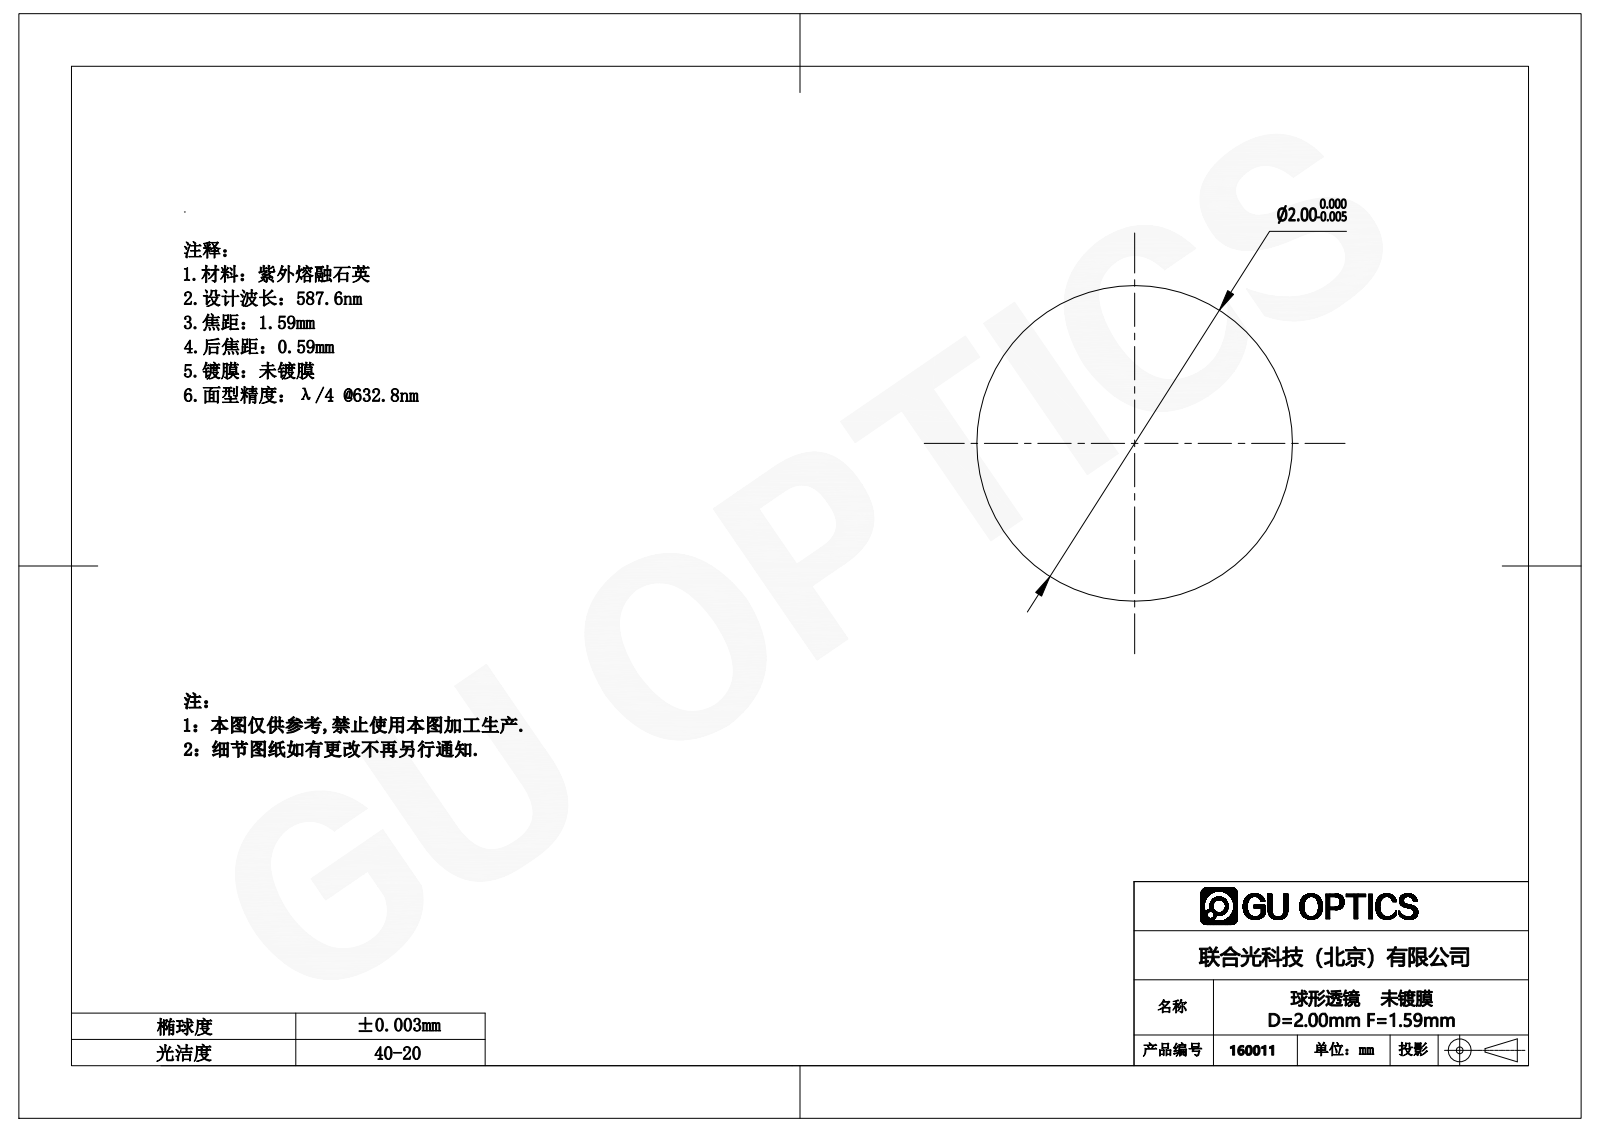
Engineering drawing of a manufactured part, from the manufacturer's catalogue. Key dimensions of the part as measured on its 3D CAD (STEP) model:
Part name (STEP PRODUCT): 160001
STEP written by: SolidWorks 2016 (CONFIG_CONTROL_DESIGN)
Units: millimetres
Bodies: 1 solid, 2 faces (0 planar, 0 cylindrical, 2 other)
Overall size (bounding box): 2 × 2 × 2
Volume: 4 mm³ · Surface area: 13 mm²
